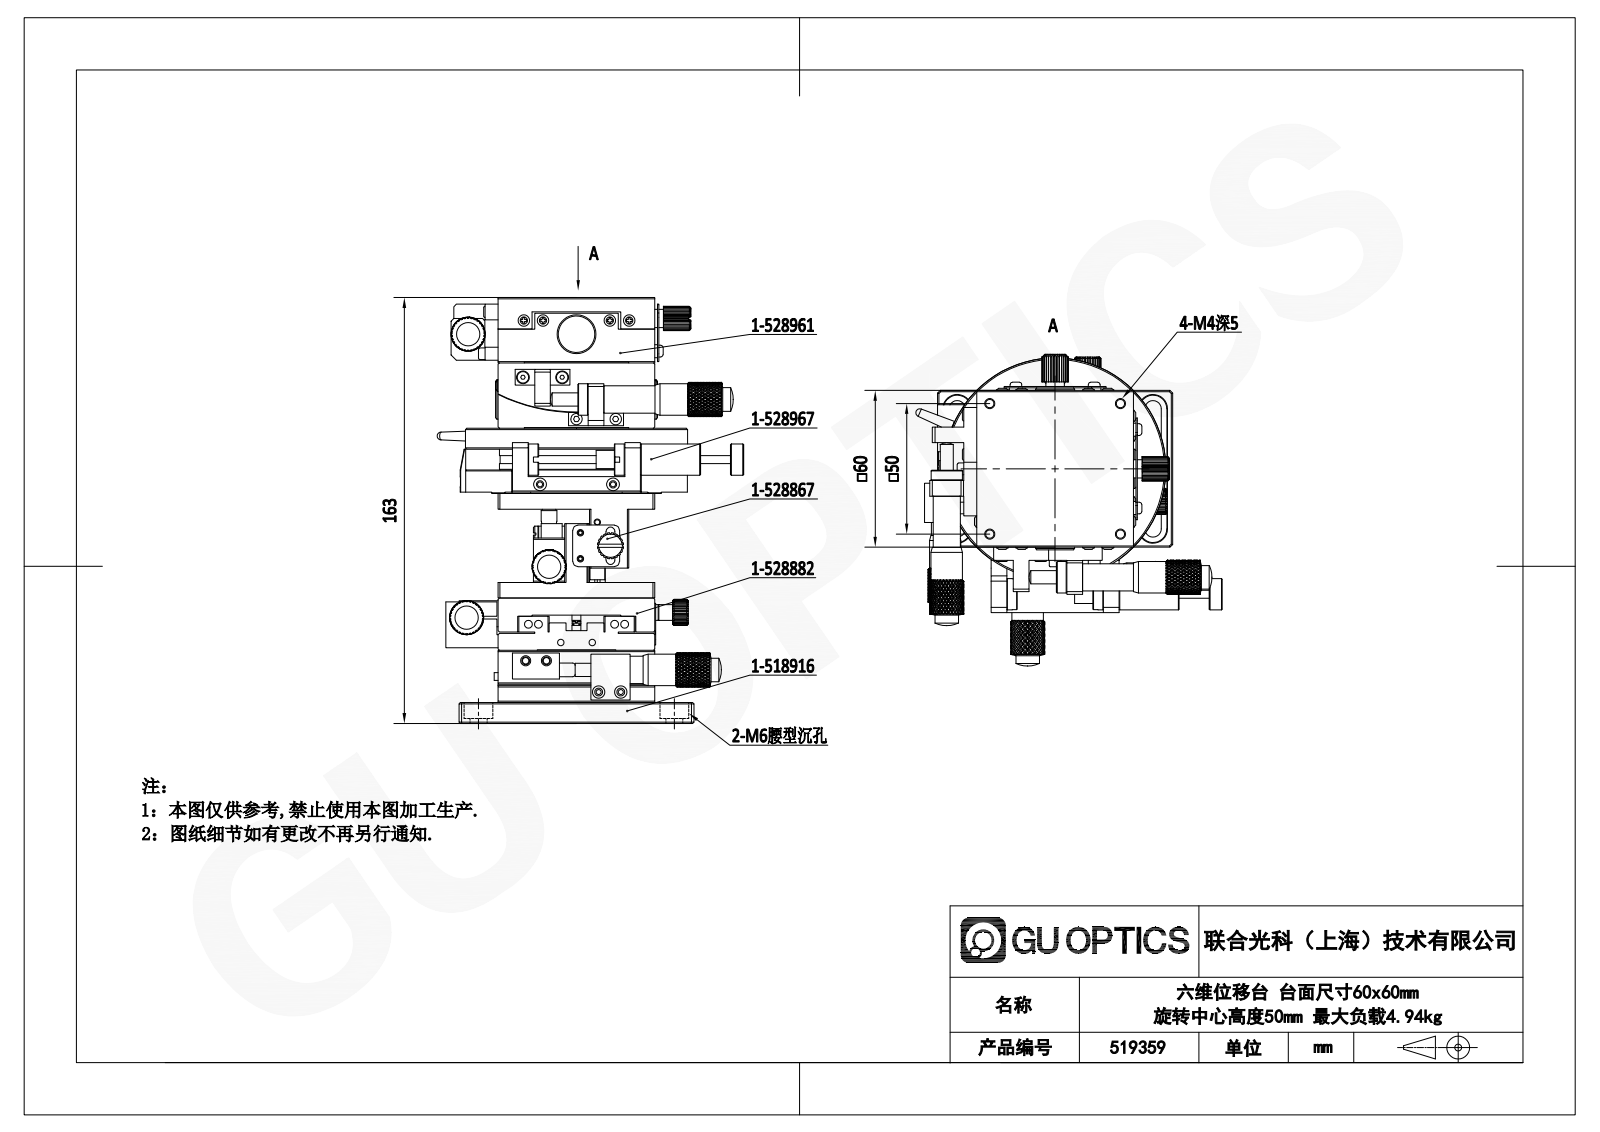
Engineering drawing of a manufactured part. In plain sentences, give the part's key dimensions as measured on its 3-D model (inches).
The part is named "ELF01-85; 528961; 528882; 528866 (+2 more)". Its 3-D file was written by "SolidWorks 2020 (CONFIG_CONTROL_DESIGN)". It is 20 solids with 11764 faces: 1581 planar, 2659 cylindrical and 7524 other. Overall it measures 6.417 by 5.055 by 4.98 inches. Its volume is 25.71 cubic inches and its surface area 356.2 square inches. Round holes: 49 of diameter 0.098, 40 of diameter 0.173, 38 of diameter 0.079, 27 of diameter 0.062, 24 of diameter 0.097, 22 of diameter 0.236, 18 of diameter 0.126, 13 of diameter 0.118, 13 of diameter 0.197, 10 of diameter 0.062, 9 of diameter 0.128, 8 of diameter 0.11. Round bosses or shafts: 20 of diameter 0.177, 14 of diameter 0.118, 8 of diameter 0.197, 6 of diameter 0.236, 5 of diameter 0.513, 5 of diameter 0.474, 4 of diameter 0.413, 4 of diameter 0.354. Partial cylindrical surfaces (rounded edges, fillets, slot ends): 32 of radius 0.018, 28 of radius 0.079, 9 of radius 0.118, 8 of radius 0.069, 4 of radius 0.025, 4 of radius 0.124, 4 of radius 0.197, 4 of radius 0.209. The main face-to-face distances are 0.984, 2.362, 0.315, 0.787, 3.819, 1.299, 1.575, 4.134, 1.969, 0.512. The hole center spacings are 0.591, 1.969, 0.835, 0.652, 1.427, 1.181, 1.182, 1.213.
